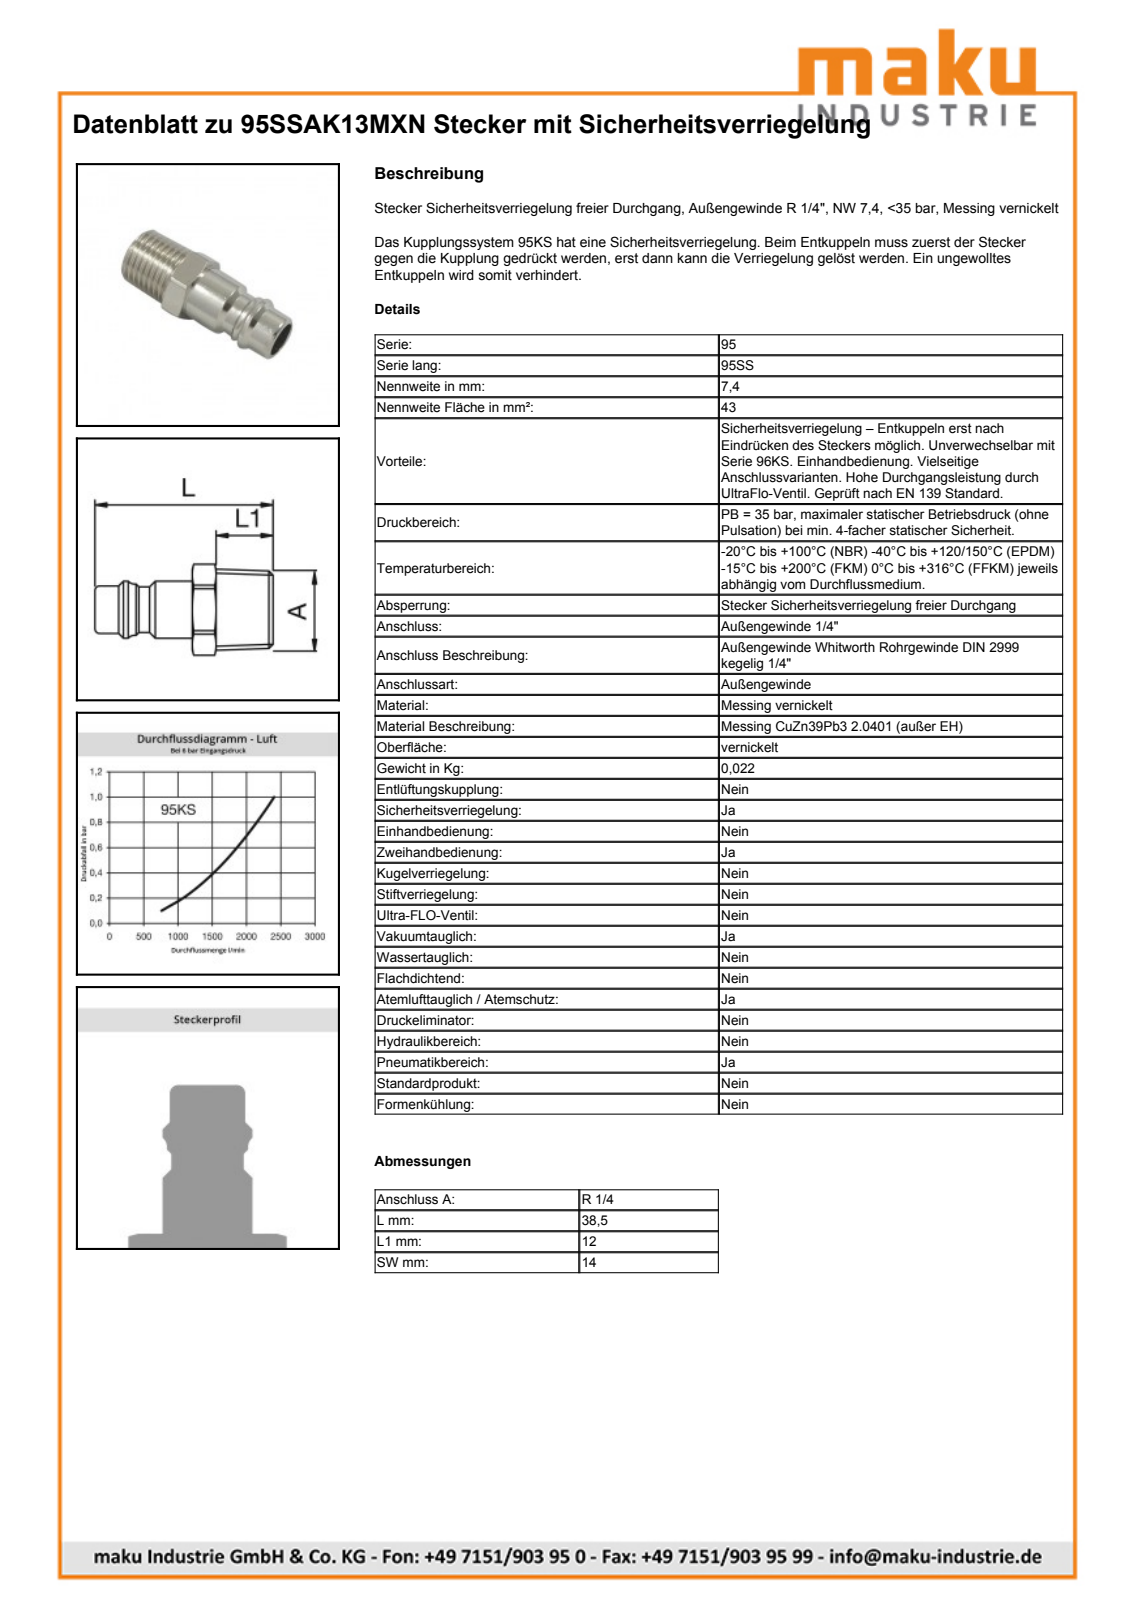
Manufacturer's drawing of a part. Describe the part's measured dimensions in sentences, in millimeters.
The part is named "D110897". Its 3-D file was written by "Autodesk Inventor 2013 (AUTOMOTIVE_DESIGN)". It is 1 solid with 41 faces: 10 planar, 12 cylindrical and 19 other. Overall it measures 37.5 by 15.8 by 14 millimeters. Its volume is 2 783 cubic millimeters and its surface area 2 516 square millimeters. Round holes: 1 of diameter 7.4. Round bosses or shafts: 1 of diameter 11.95, 1 of diameter 10.8, 1 of diameter 9.9, 1 of diameter 9.6. Partial cylindrical surfaces (rounded edges, fillets, slot ends): 1 of radius 7.9. The main face-to-face distances are 14, 16.9, 12, 4.9, 37.5, 25.5, 20.6.
